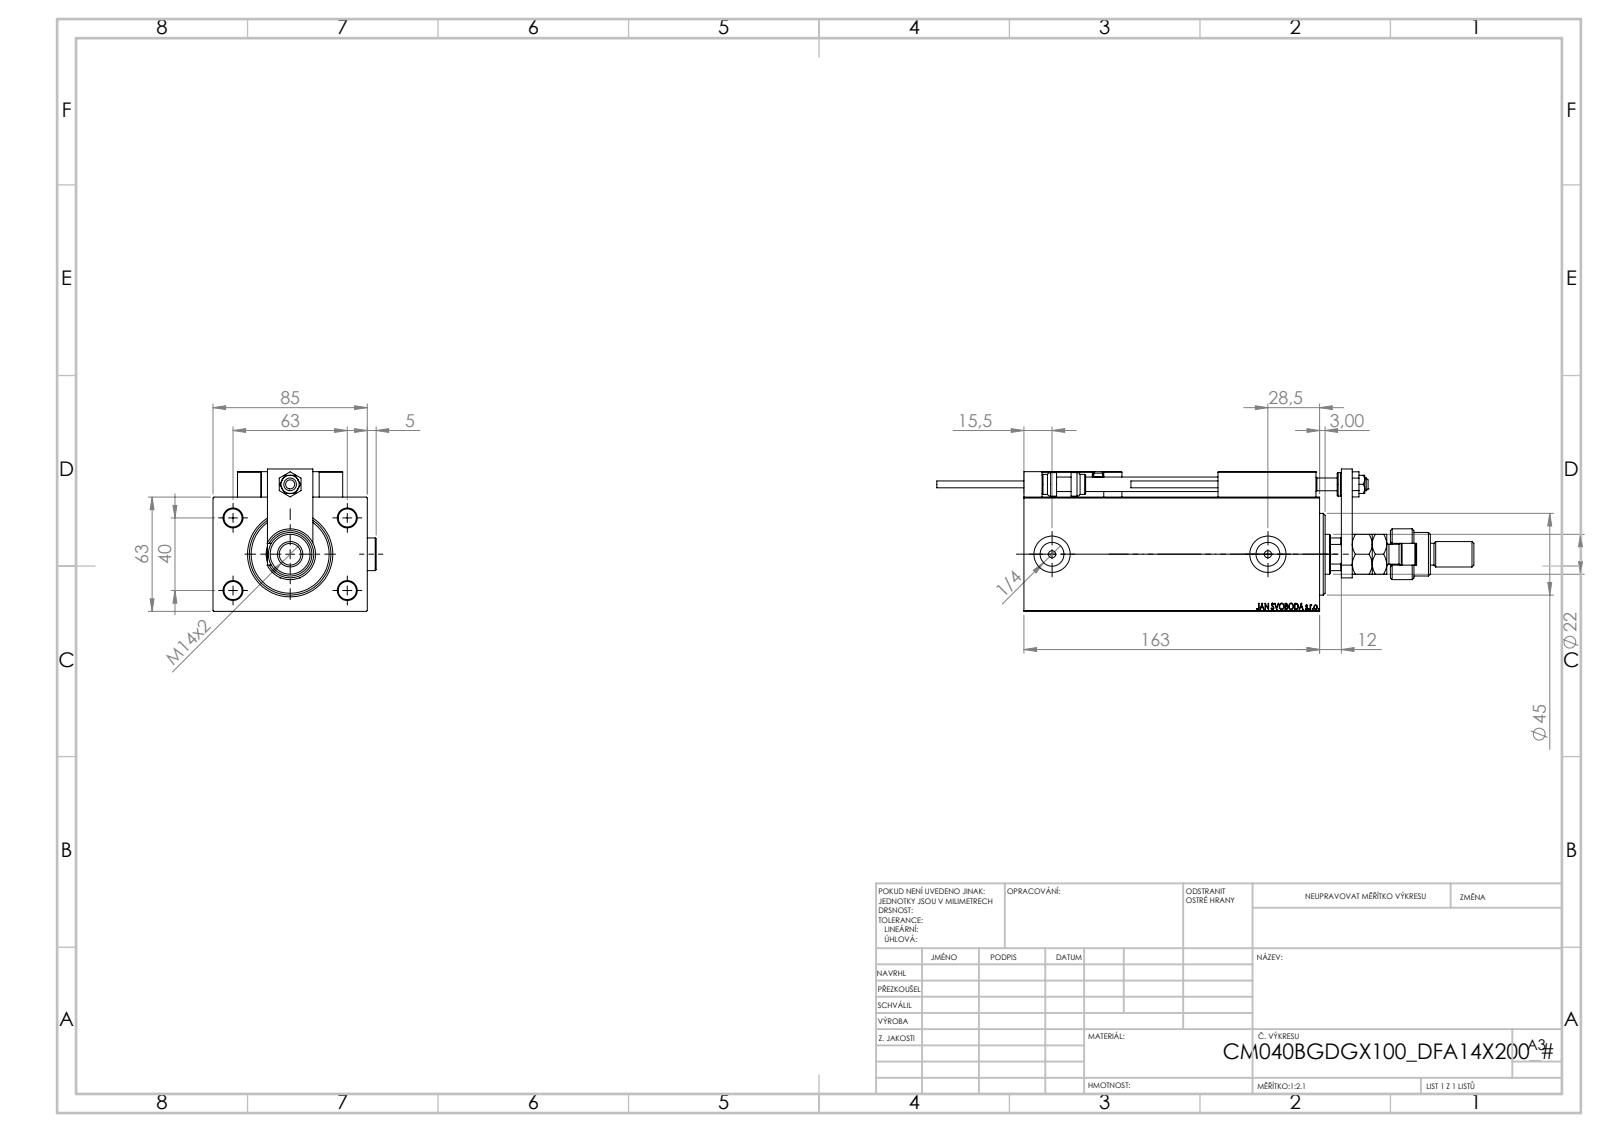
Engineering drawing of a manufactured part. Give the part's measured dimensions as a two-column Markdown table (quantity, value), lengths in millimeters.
| quantity | value |
| --- | --- |
| part name | SWITCH X; ZARAZKA; NUT_D10; FEMALE_PART_FOR_DFA (+8 more) |
| STEP written by | SolidWorks 2019 (CONFIG_CONTROL_DESIGN) |
| units | millimeters |
| bodies | 28 solids, 1457 faces (623 planar, 213 cylindrical, 621 other) |
| overall size | 296 × 89.9 × 78.5 |
| volume | 845 949 mm³ |
| surface area | 144 118 mm² |
| round holes (diameter × count) | 4 × 6, 8 × 5, 3.2 × 4, 10 × 4, 5 × 2, 13.16 × 2, 20 × 2, 7 × 1, 12.5 × 1, 16.5 × 1, 22 × 1, 25.5 × 1 |
| round bosses / shafts (diameter × count) | 18 × 3, 11 × 2, 5 × 2, 3.8 × 2, 28 × 1, 24 × 1, 14 × 1, 13 × 1 |
| partial cylindrical surfaces (radius × count) | 0.3 × 30, 3 × 2, 9.75 × 1, 10.5 × 1 |
| main face-to-face distances | 63, 85, 12, 151, 163, 14, 30, 18, 77, 15 |
| hole center spacings | 37.31, 11.37, 20, 29.59, 29.69, 36.06, 36.53, 40 |
